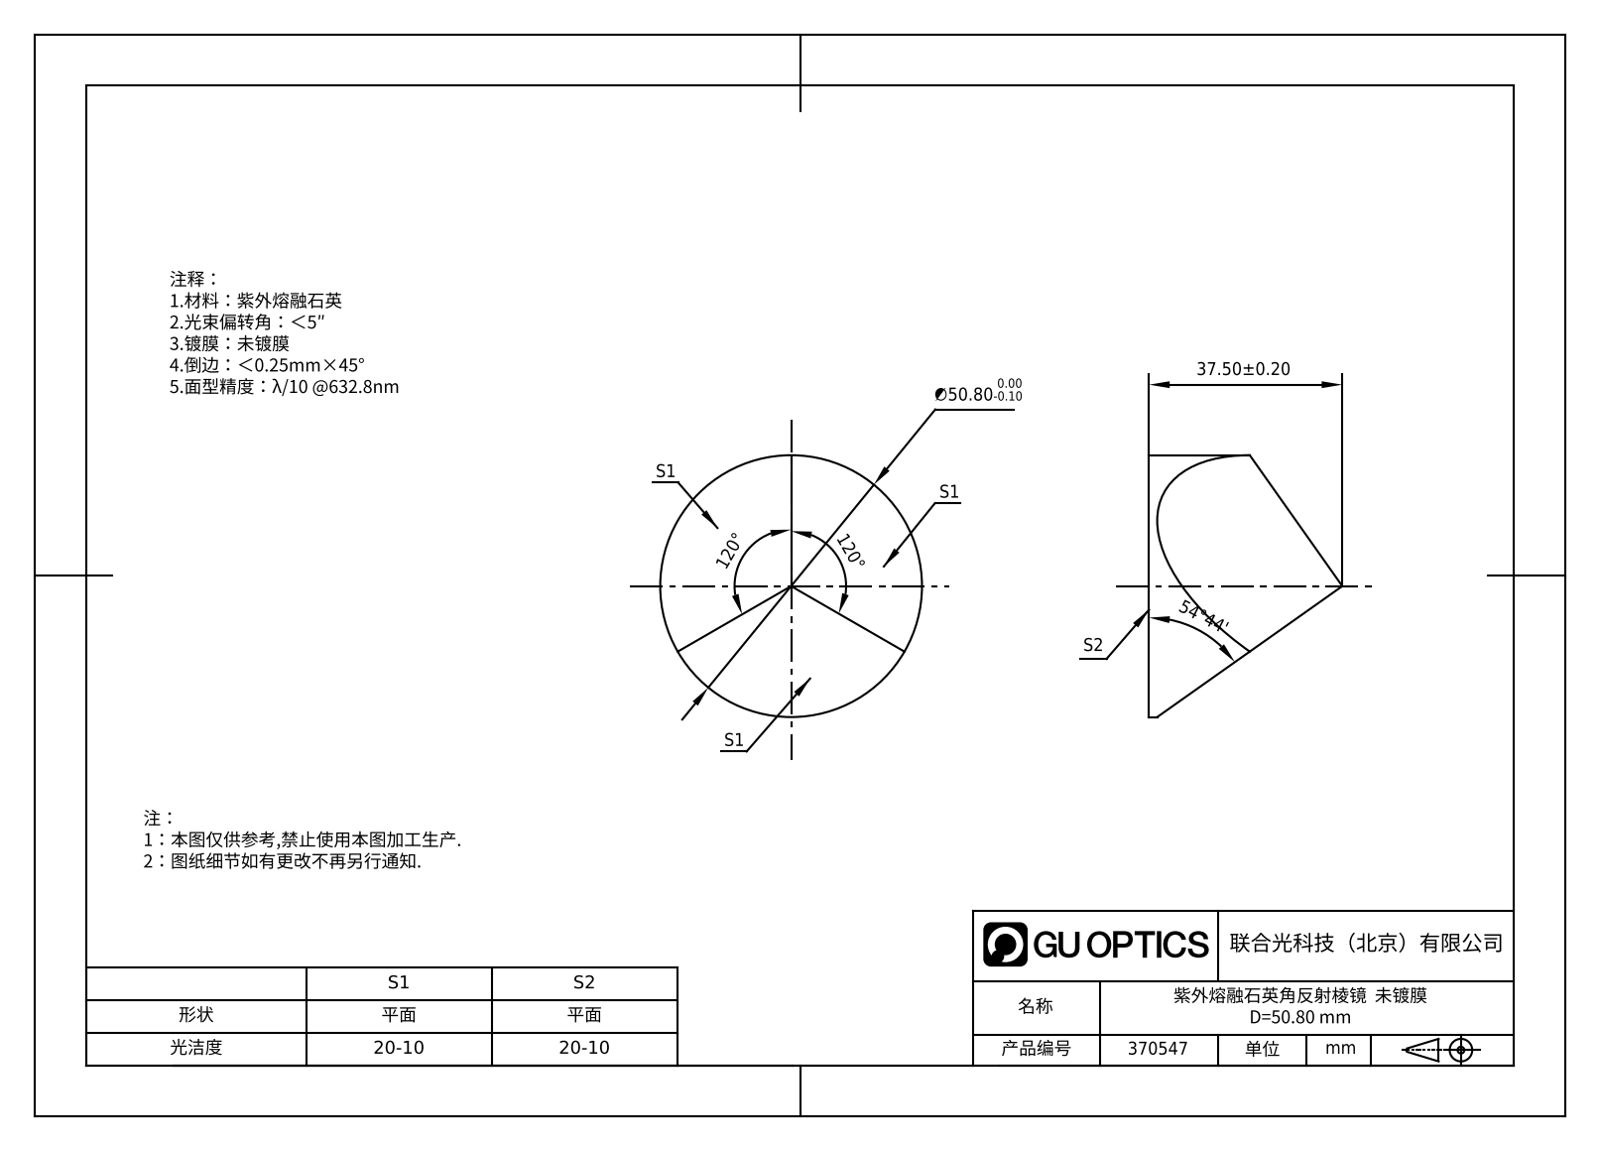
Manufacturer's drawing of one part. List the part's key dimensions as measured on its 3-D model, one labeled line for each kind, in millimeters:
Part name (STEP PRODUCT): GP26-050-1
STEP written by: SolidWorks 2022 (AUTOMOTIVE_DESIGN)
Units: millimetres
Bodies: 1 solid, 12 faces (8 planar, 2 cylindrical, 2 other)
Overall size (bounding box): 50.8 × 50.8 × 37.38
Volume: 35 866 mm³ · Surface area: 6 766 mm²
Round bosses / shafts (diameter × count): ⌀50.8 ×1
Main face-to-face distances: 37.39
